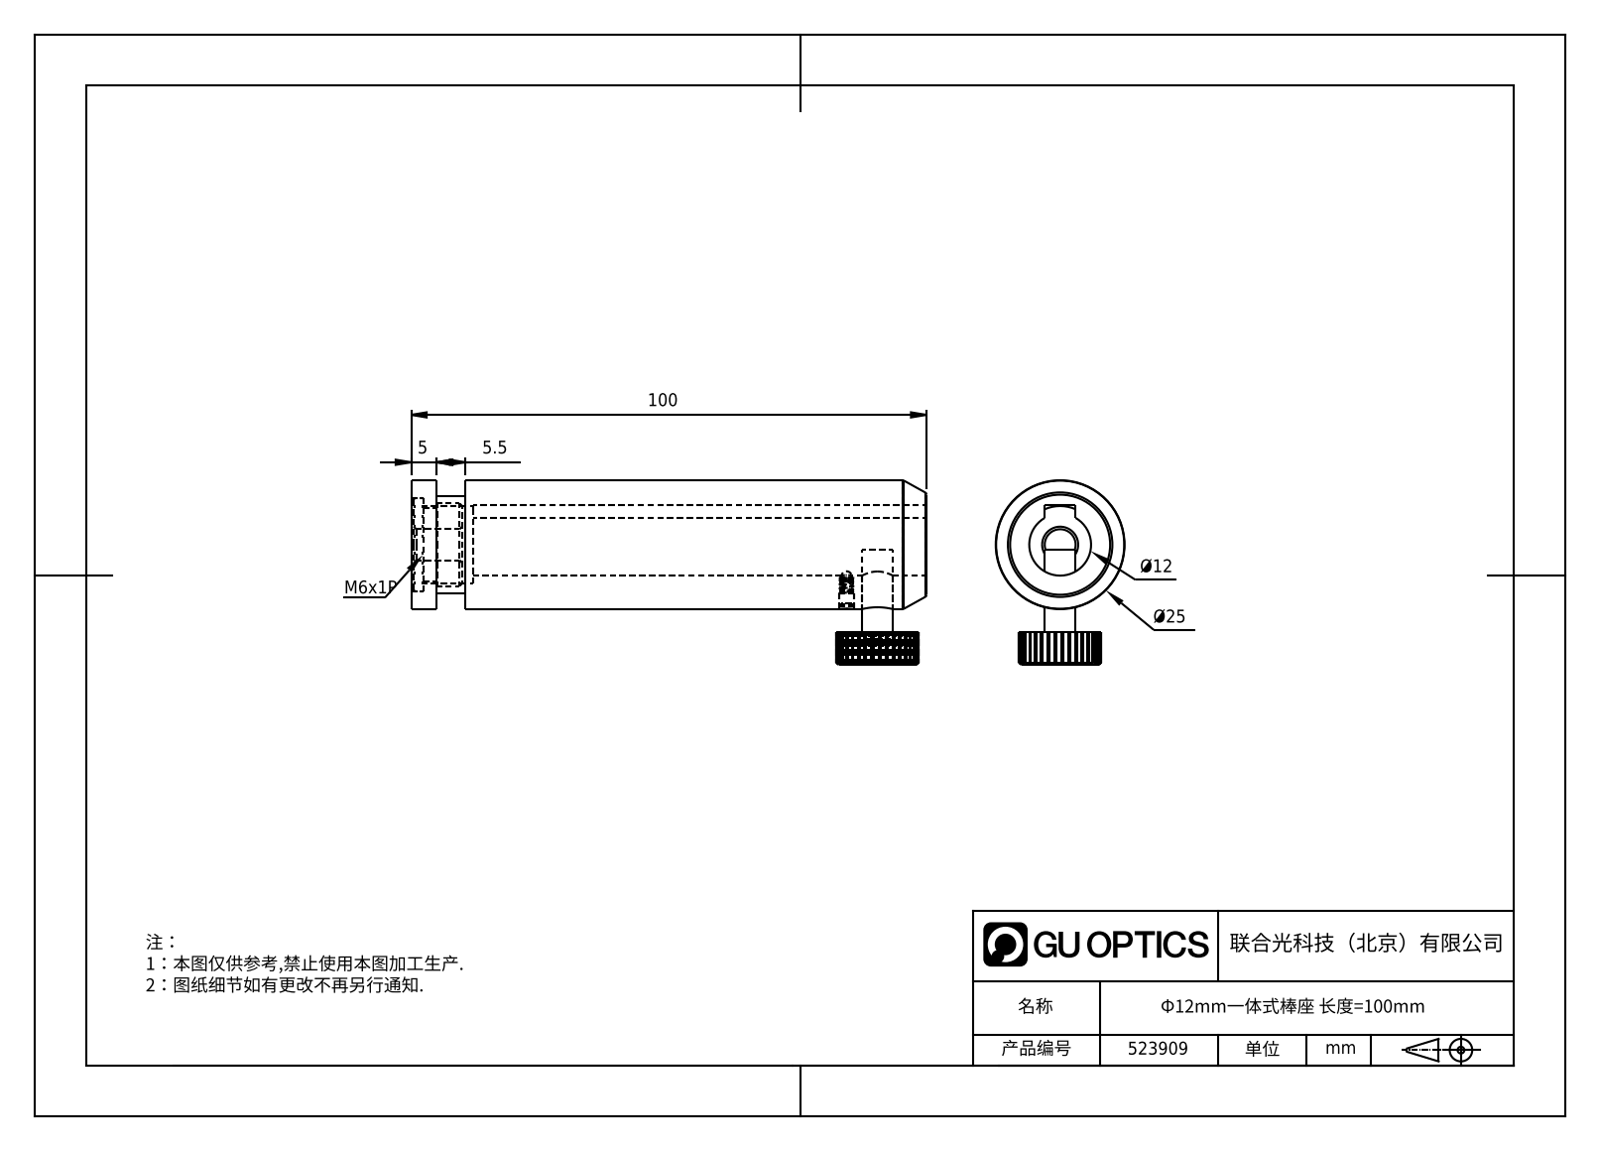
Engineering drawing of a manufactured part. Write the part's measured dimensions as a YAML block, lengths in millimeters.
part_name: "M-PHF-12-100"
step_written_by: "SolidWorks 2019 (CONFIG_CONTROL_DESIGN)"
units: millimeters
bodies: {solids: 3, faces: 219, planar: 114, cylindrical: 83, other: 22}
overall_size: [100, 35.84, 25]
volume: 37167
surface_area: 14456
round_holes:
  - {diameter: 2.1, count: 1}
  - {diameter: 2.12, count: 1}
  - {diameter: 2.6, count: 1}
  - {diameter: 6, count: 1}
  - {diameter: 12, count: 1}
  - {diameter: 15, count: 1}
  - {diameter: 18, count: 1}
round_bosses_or_shafts:
  - {diameter: 25, count: 1}
  - {diameter: 19, count: 1}
  - {diameter: 14.3, count: 1}
  - {diameter: 6, count: 1}
  - {diameter: 3, count: 1}
  - {diameter: 2.16, count: 1}
  - {diameter: 0.99, count: 1}
partial_cylinders:
  - {radius: 8, count: 1}
face_to_face_distances: [5, 6, 5.5, 10.5, 4.5, 0.5, 10, 100, 99.5, 95]
